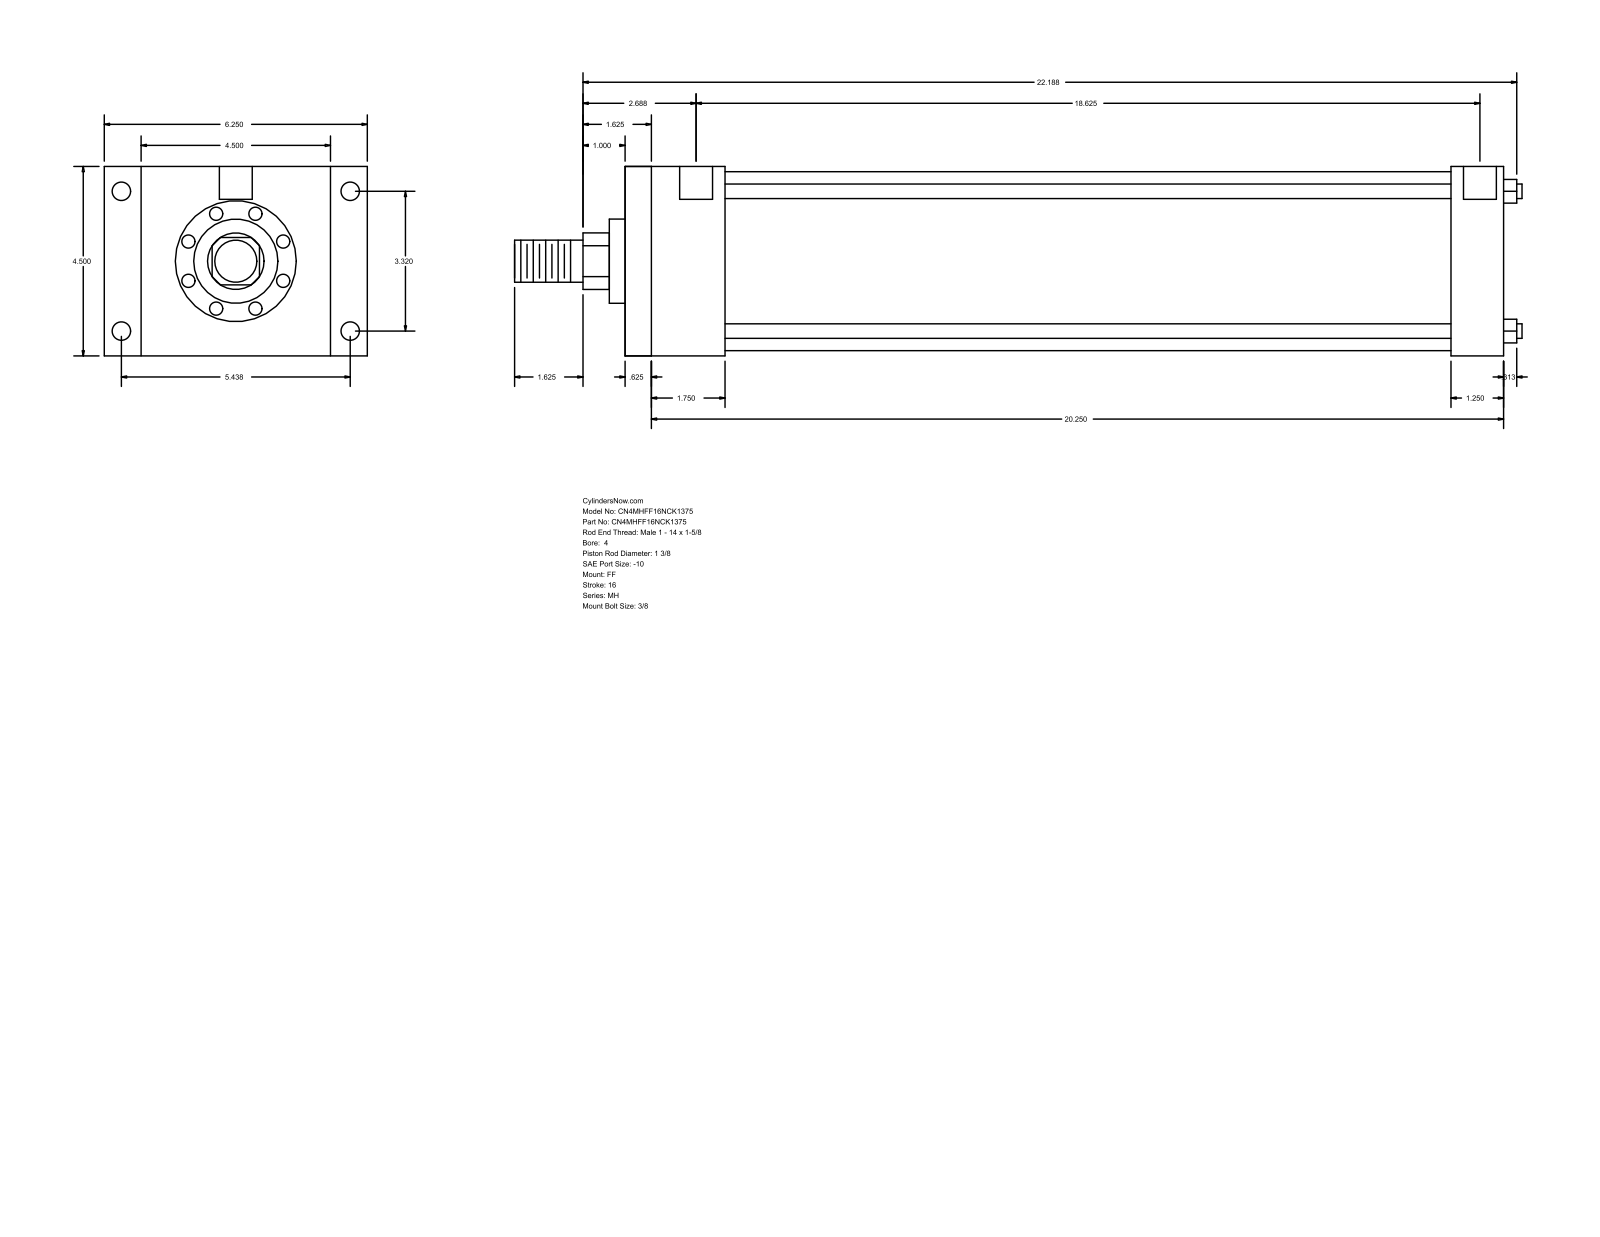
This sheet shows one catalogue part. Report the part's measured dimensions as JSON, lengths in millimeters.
{"part_name": "MH_FF__0400_1.375", "step_written_by": "GSSL Pune (CONFIG_CONTROL_DESIGN)", "units": "millimeters", "bodies": {"solids": 0, "faces": 92, "planar": 64, "cylindrical": 28, "other": 0}, "overall_size": [608.01, 158.75, 114.3], "round_holes": [[8.73, 4], [11.13, 4], [19.84, 2]], "round_bosses_or_shafts": [[8.76, 4], [107.95, 1], [50.8, 1], [34.92, 1], [25.4, 1]], "partial_cylinders_radius": [[17.06, 1]], "face_to_face_distances": [114.3, 530.22, 15.87, 514.35, 60.32, 44.45, 469.9, 498.48, 482.61, 438.16], "hole_center_spacings": [84.32, 138.12, 161.82, 476.25, 1.58, 1.59, 473.08, 474.66]}
